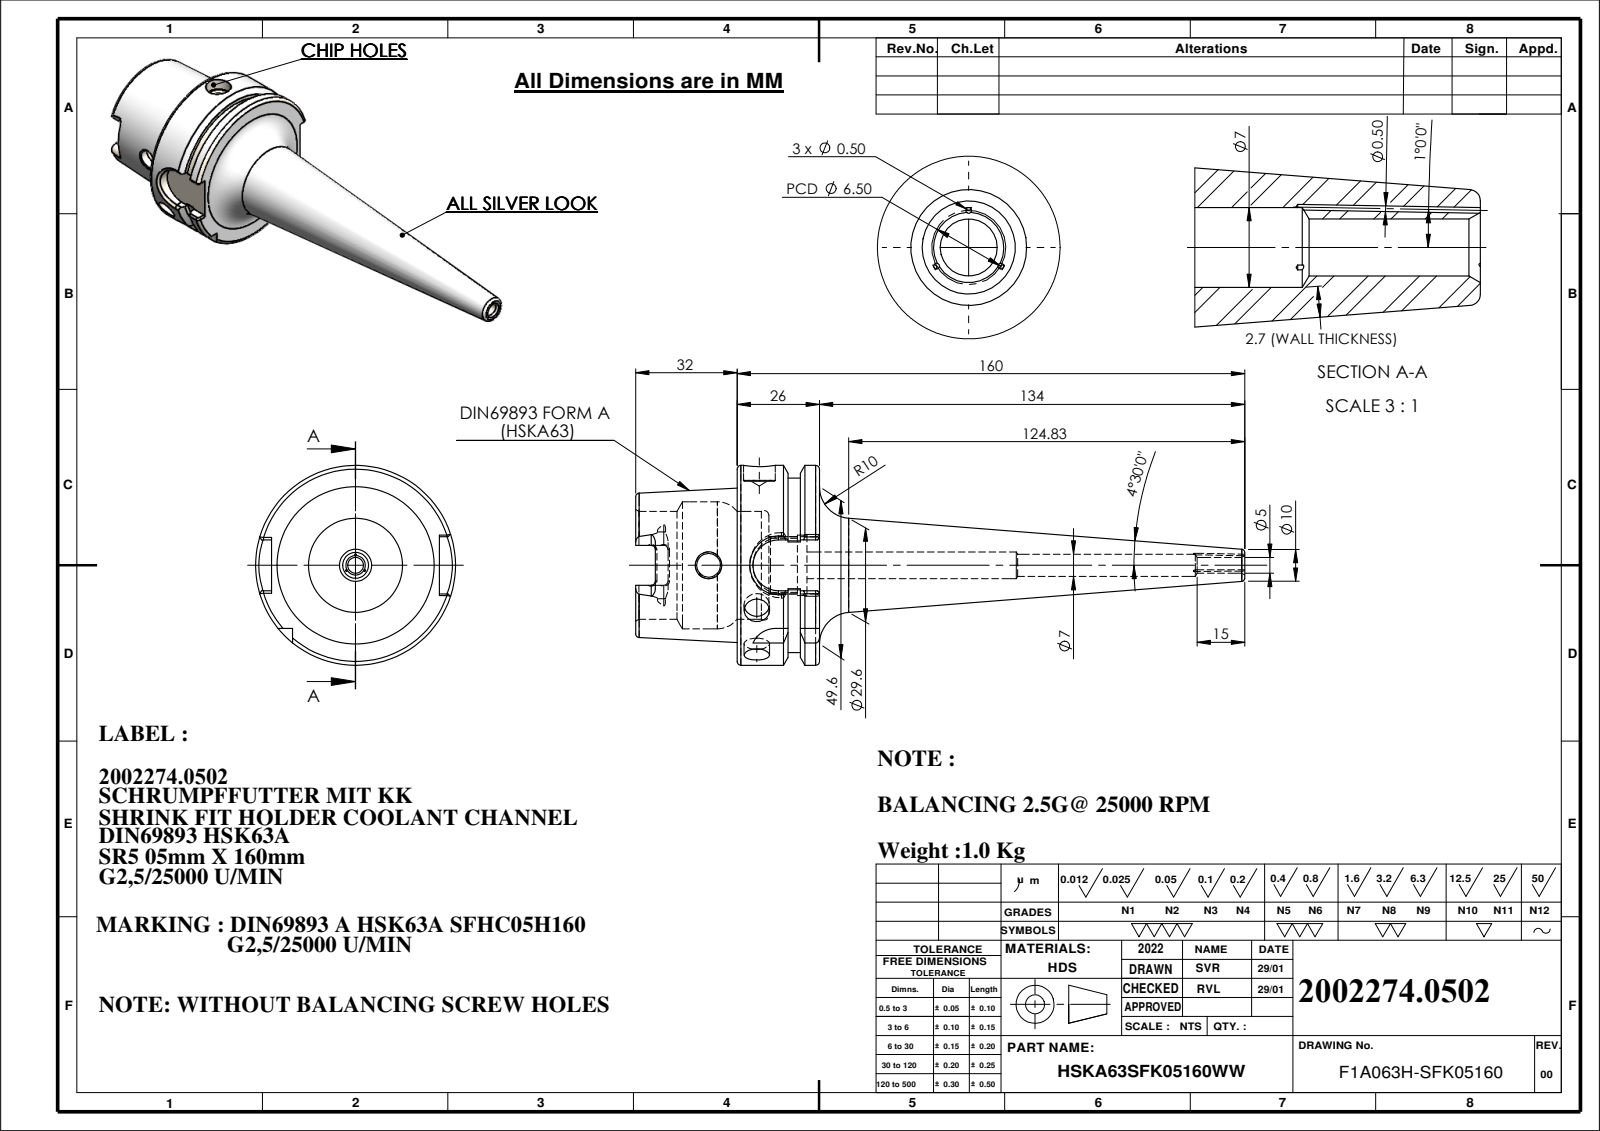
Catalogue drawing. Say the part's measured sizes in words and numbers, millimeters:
The part is named "9163A-SR505160". Its 3-D file was written by "SolidWorks 2018 (CONFIG_CONTROL_DESIGN)". It is 1 solid with 178 faces: 49 planar, 55 cylindrical and 74 other. Overall it measures 192 by 63 by 63 millimeters. Its volume is 125 188 cubic millimeters and its surface area 33 267 square millimeters. Round holes: 3 of diameter 0.5, 2 of diameter 8, 1 of diameter 4.99, 1 of diameter 7, 1 of diameter 7.5, 1 of diameter 8.4, 1 of diameter 10, 1 of diameter 17, 1 of diameter 19, 1 of diameter 34, 1 of diameter 40. Round bosses or shafts: 1 of diameter 63, 1 of diameter 55. Partial cylindrical surfaces (rounded edges, fillets, slot ends): 6 of radius 1.3, 4 of radius 2.88, 2 of radius 8, 1 of radius 9. The main face-to-face distances are 25.95, 10, 15.95, 32, 42, 57.95, 52.9, 54, 22, 12.
